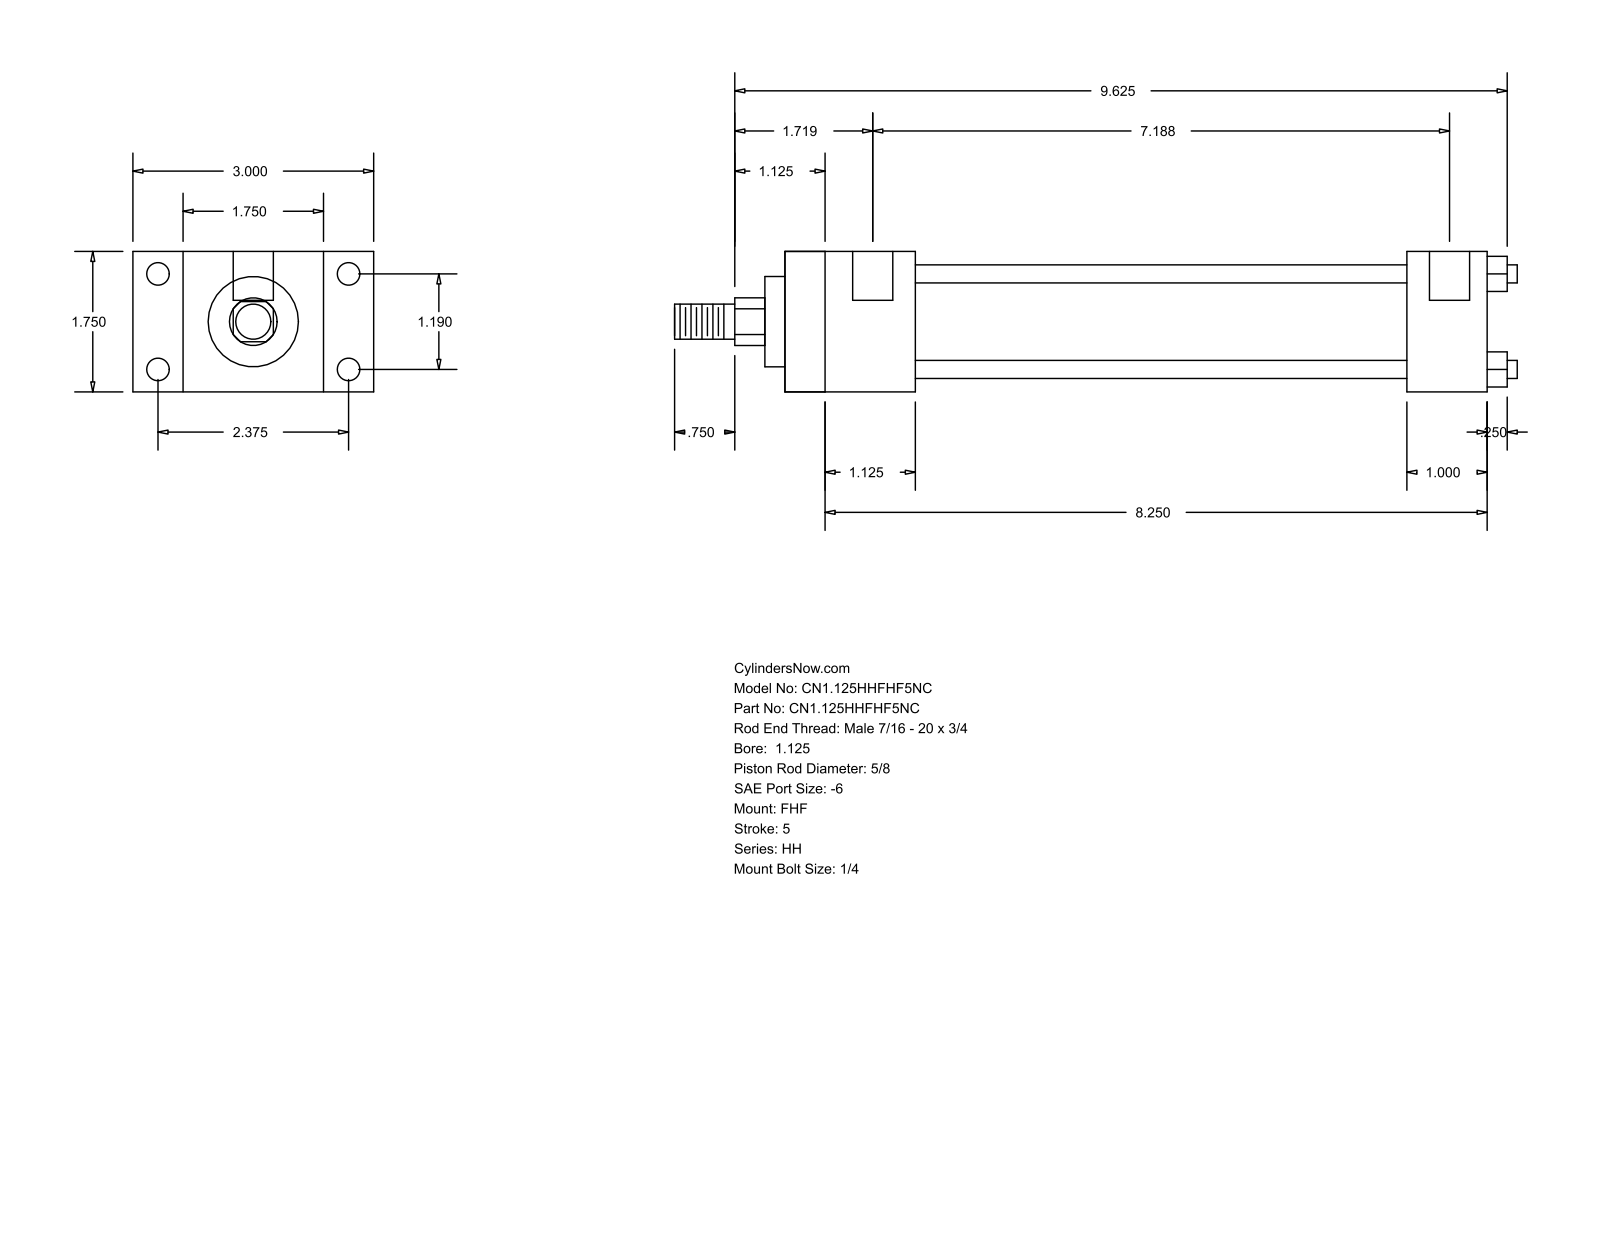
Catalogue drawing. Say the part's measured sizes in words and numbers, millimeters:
The part is named "HH_FHF__0112_0.625". Its 3-D file was written by "GSSL Pune (CONFIG_CONTROL_DESIGN)". It is 0 solids with 88 faces: 60 planar, 28 cylindrical and 0 other. Overall it measures 266.7 by 76.2 by 44.45 millimeters. Round holes: 4 of diameter 5.56, 4 of diameter 7.14, 2 of diameter 12.7. Round bosses or shafts: 4 of diameter 5.71, 1 of diameter 34.92, 1 of diameter 28.57, 1 of diameter 15.88, 1 of diameter 11.11. Partial cylindrical surfaces (rounded edges, fillets, slot ends): 1 of radius 7.54. The main face-to-face distances are 44.46, 15.87, 60.33, 41.27, 76.2, 222.24, 180.97, 25.4, 196.84, 155.57. The hole center spacings are 30.22, 60.32, 67.47, 179.39, 3.17, 182.56.
